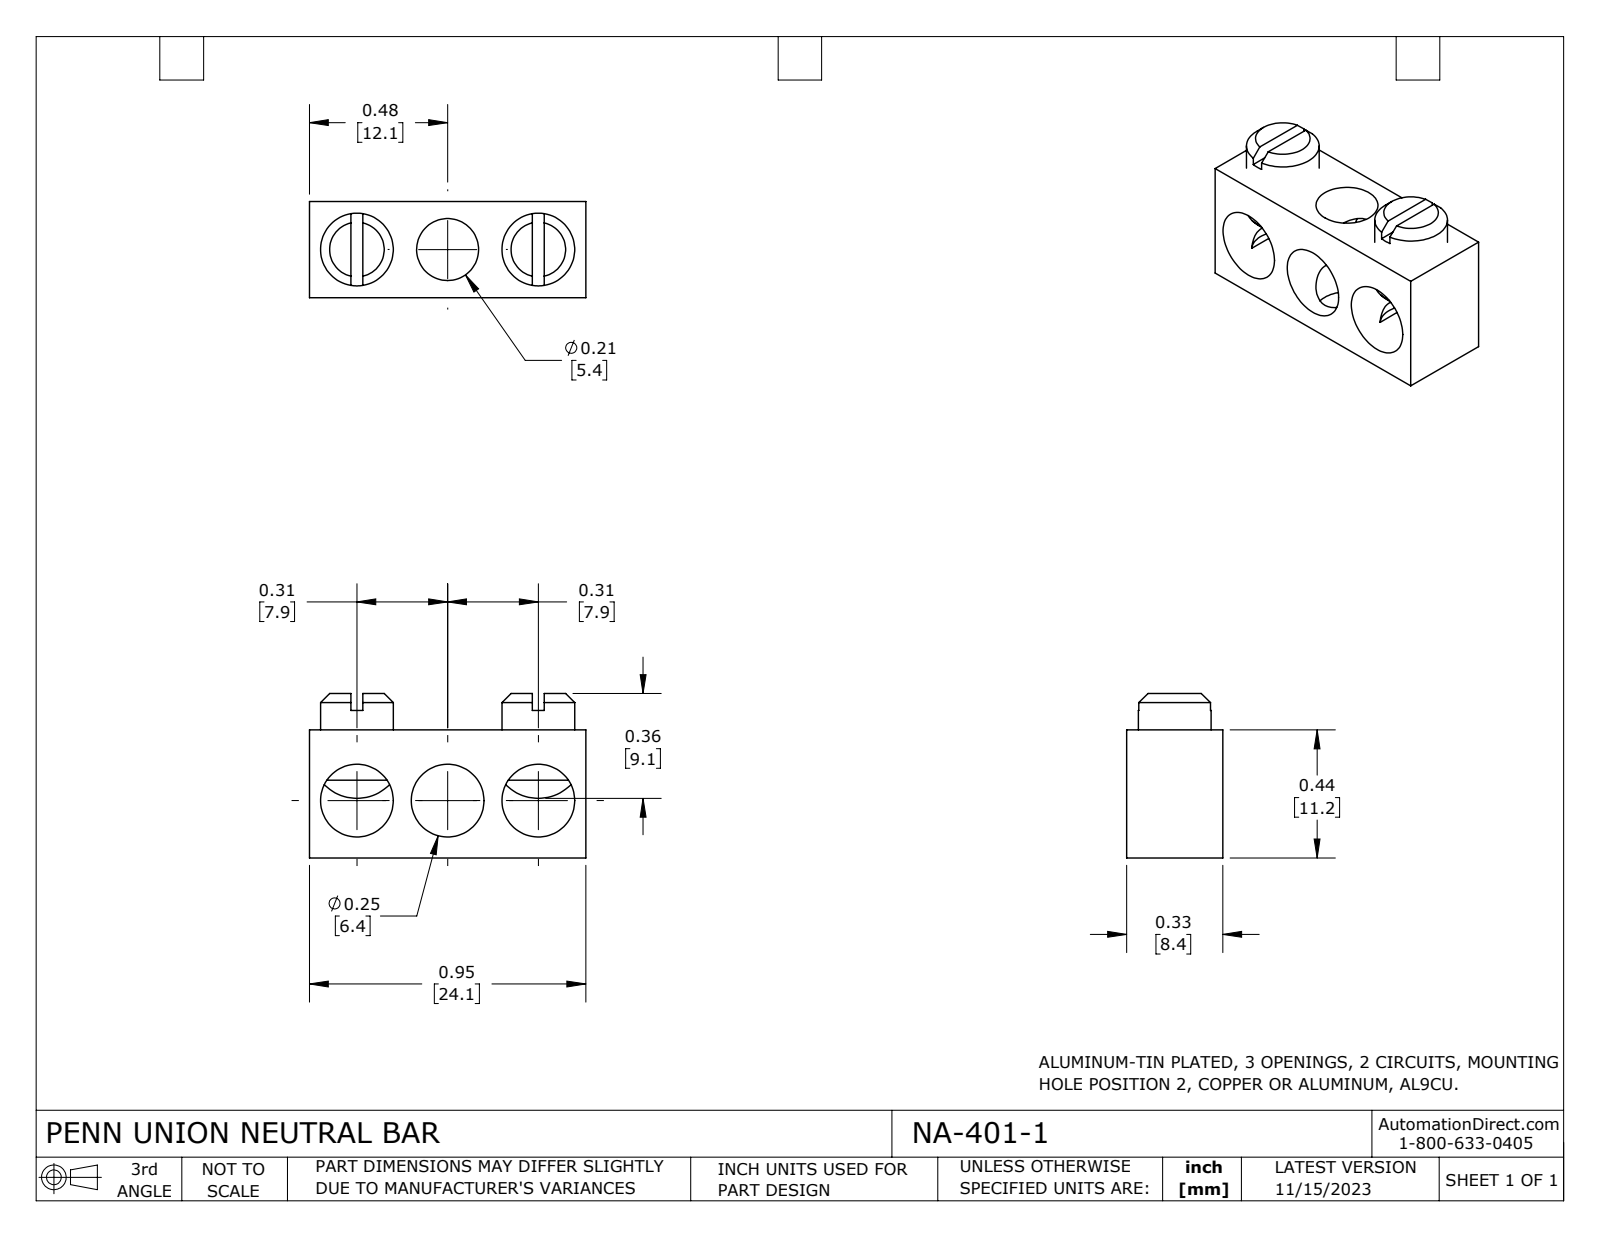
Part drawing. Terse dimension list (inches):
name: NA-401-1
written by: SolidWorks 2023 (CONFIG_CONTROL_DESIGN)
unit: in
bodies: 3 solids, 52 faces (20 planar, 22 cylindrical, 10 other)
size: 0.95 × 0.565 × 0.331
volume: 0.103 in³; area: 3.005 in²
holes: 3× ⌀0.213, 3× ⌀0.25
bosses: 2× ⌀0.25
face distances: 0.331, 0.439, 0.95, 0.565, 0.125, 0.624, 0.041, 0.507, 0.067, 0.058
hole spacings: 0.312, 0.624
